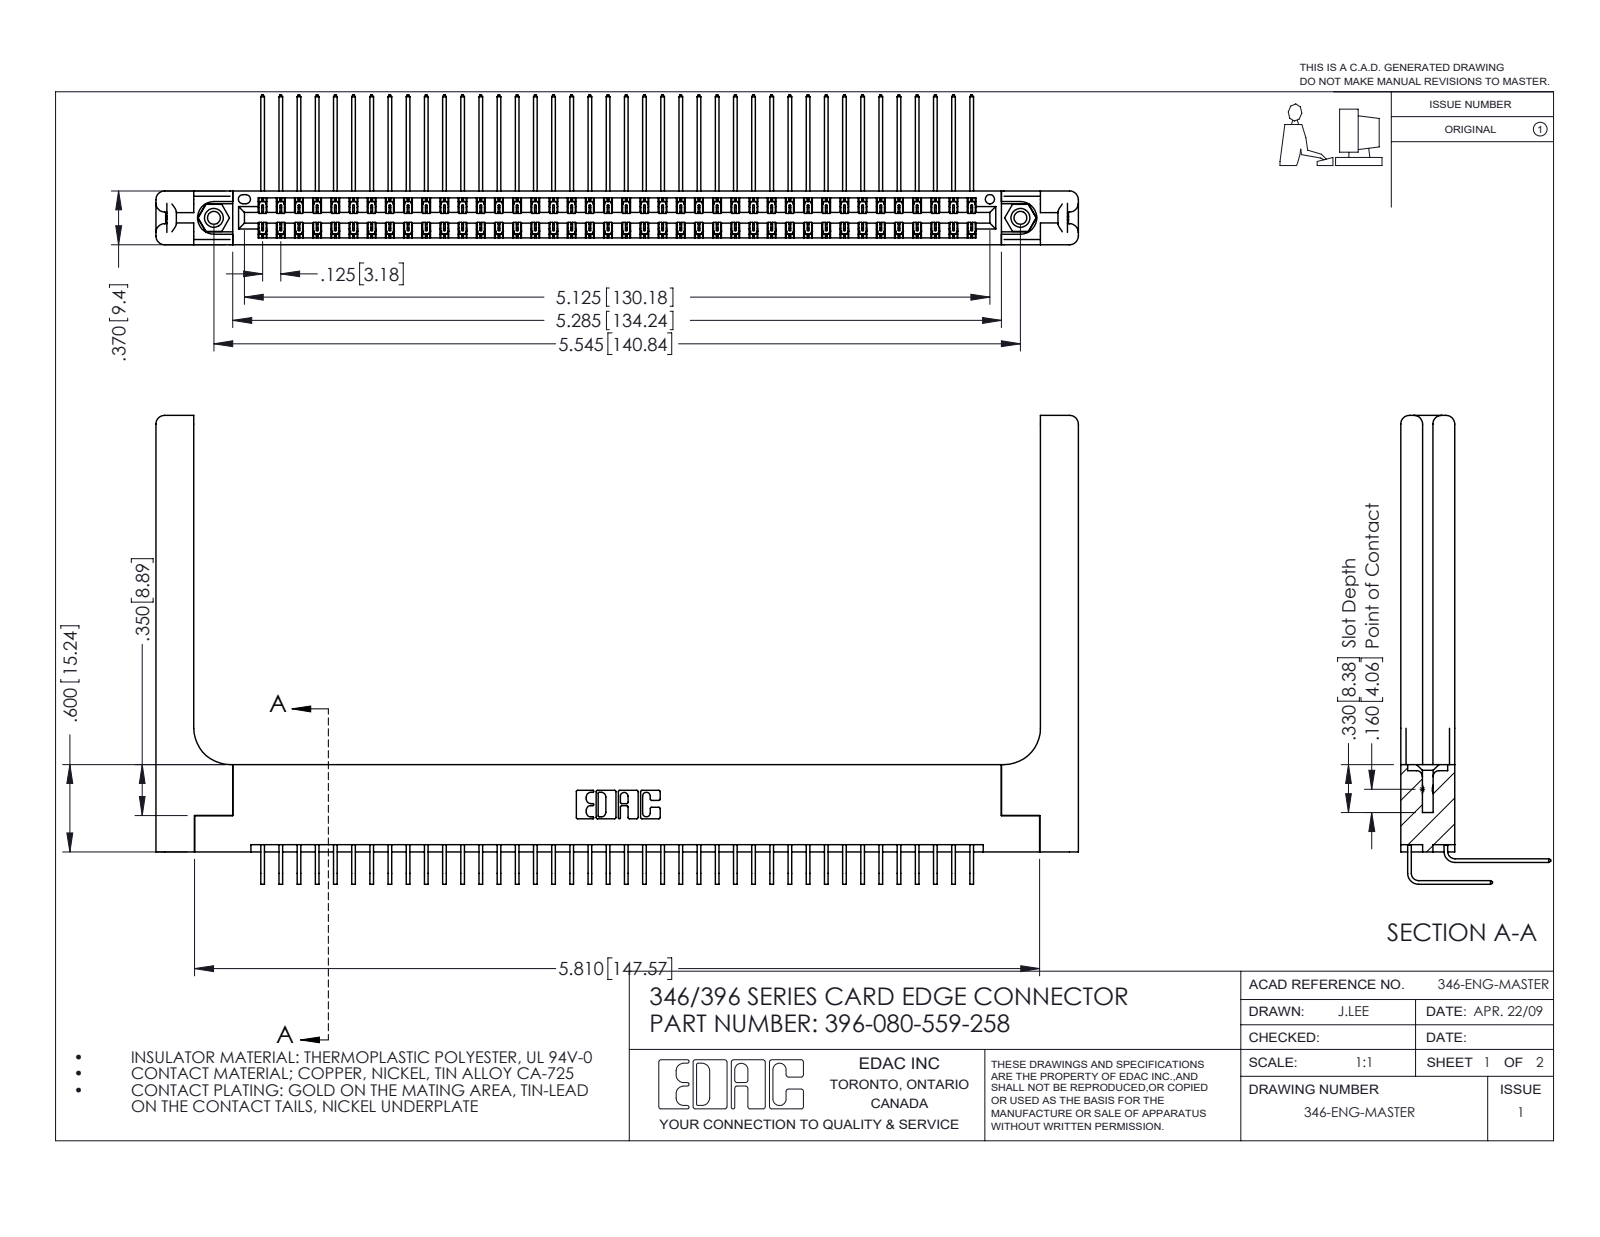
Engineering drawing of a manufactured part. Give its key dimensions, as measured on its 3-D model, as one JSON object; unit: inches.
{"part_name": "396-080-559-258; 346-220-058_345-220-058; 346 Part_Flush Mounting Lugs - 0.156 Dia-TH; 345-292-001_559 Tail - 2 (+2 more)", "step_written_by": "SolidWorks 2016 (CONFIG_CONTROL_DESIGN)", "units": "inches", "bodies": {"solids": 85, "faces": 4698, "planar": 3184, "cylindrical": 1454, "other": 60}, "overall_size": [6.341, 3.223, 1.03], "volume_in3": 1.443, "surface_area_in2": 45.5, "round_holes": [[0.089, 2], [0.125, 2], [0.156, 2], [0.064, 1]], "round_bosses_or_shafts": [[0.155, 2]], "partial_cylinders_radius": [[0.006, 120], [0.01, 22], [0.06, 16], [0.007, 6], [0.031, 6], [0.026, 3], [0.014, 2], [0.022, 2]], "face_to_face_distances": [0.048, 0.322, 0.37, 0.072, 0.025, 0.15, 0.148, 0.25, 0.298, 0.275], "hole_center_spacings": [0.246, 5.336, 5.545]}
